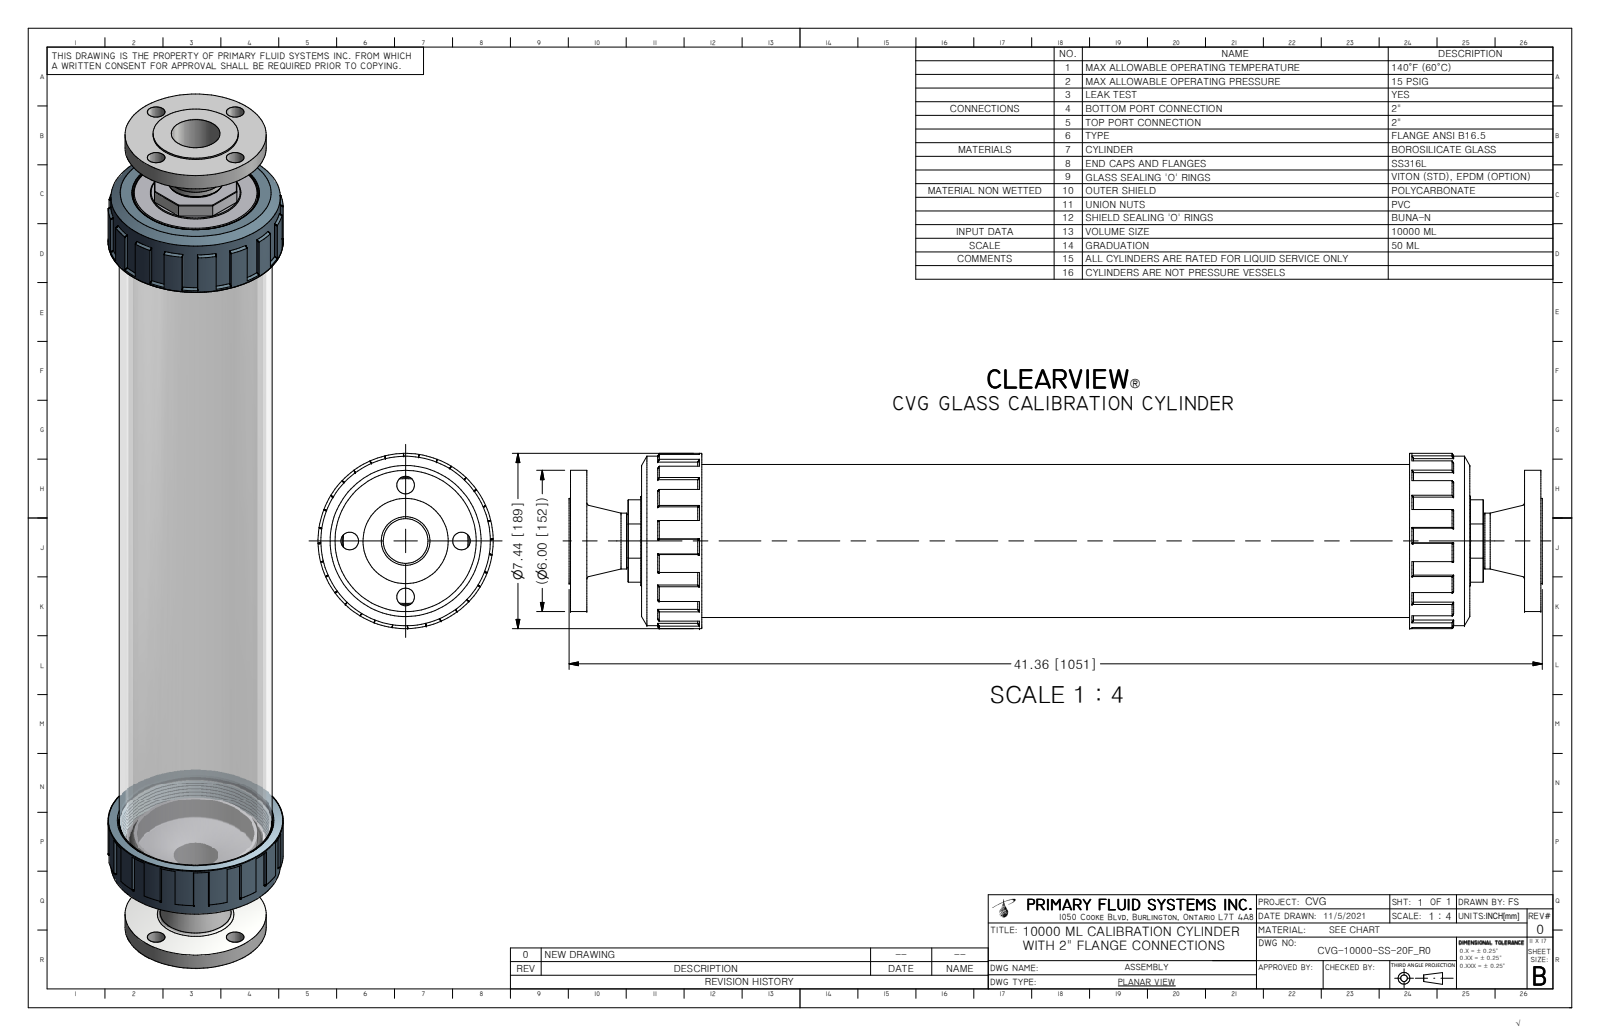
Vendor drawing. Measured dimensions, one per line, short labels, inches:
written by: Autodesk Inventor 2009 (AUTOMOTIVE_DESIGN)
unit: in
bodies: 3 solids, 385 faces (140 planar, 97 cylindrical, 148 other)
size: 41.361 × 7.445 × 7.445
volume: 127.4 in³; area: 3 215 in²
holes: 4× ⌀0.75, 1× ⌀1.9, 1× ⌀2.067, 1× ⌀2.219, 1× ⌀4.98, 1× ⌀5.315, 1× ⌀5.386, 1× ⌀5.709, 1× ⌀5.76, 1× ⌀5.97, 1× ⌀6.535
bosses: 1× ⌀7.445, 1× ⌀7.201, 1× ⌀6.5, 1× ⌀6.496, 1× ⌀6.26, 1× ⌀6.25, 1× ⌀6, 1× ⌀5.3
rounds: 2× R0.335, 2× R3.38
face distances: 2.327, 37.529, 0.69, 3.017, 38.219, 40.546, 35.202, 39.856, 5.576, 35.659
hole spacings: 2.375, 3.359, 4.75
